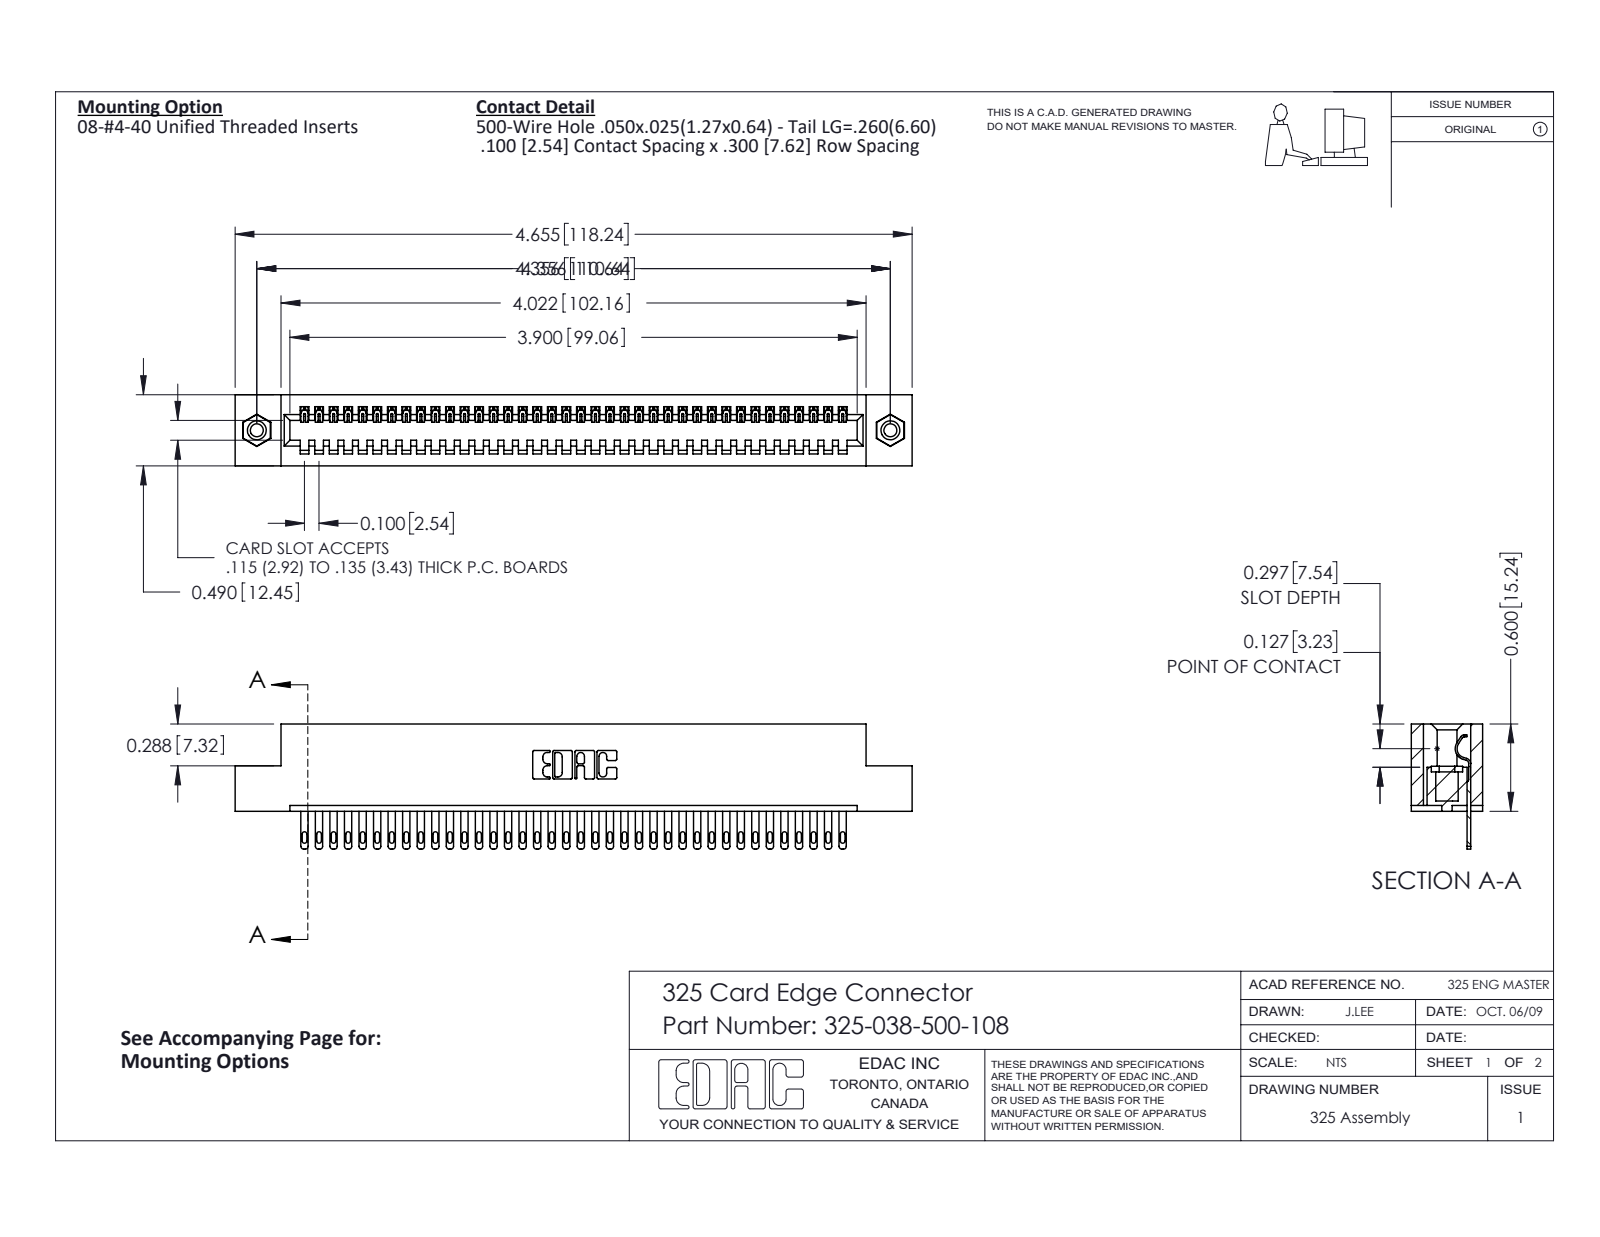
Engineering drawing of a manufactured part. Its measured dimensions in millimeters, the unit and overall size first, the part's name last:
Units: millimetres
Overall size (bounding box): 118.2 × 21.8 × 12.4
Round holes (diameter × count): ⌀2.3 ×2, ⌀3.2 ×2, ⌀4.1 ×2
Round bosses / shafts (diameter × count): ⌀3.9 ×2
Partial cylindrical surfaces — rounded edges, fillets, slot ends (radius × count): R0.2 ×76, R0.4 ×76, R0.5 ×76, R0.3 ×22, R0.2 ×6, R0.8 ×6, R0.7 ×3, R0.4 ×1
Main face-to-face distances: 2.1, 10.3, 12.4, 7.6, 2.7, 9.7, 0.6, 8.3, 14.2, 6.7
Hole centre spacings: 110.6
Volume: 15 000 mm³ · Surface area: 16 420 mm²
Bodies: 41 solids, 2226 faces (1470 planar, 740 cylindrical, 16 other)
Part name (STEP PRODUCT): 325 Part_TI; 325-292-001_325-293-100; 345-250-001_345-250-003-102; 325-038-500-108
STEP written by: SolidWorks 2016 (CONFIG_CONTROL_DESIGN)
